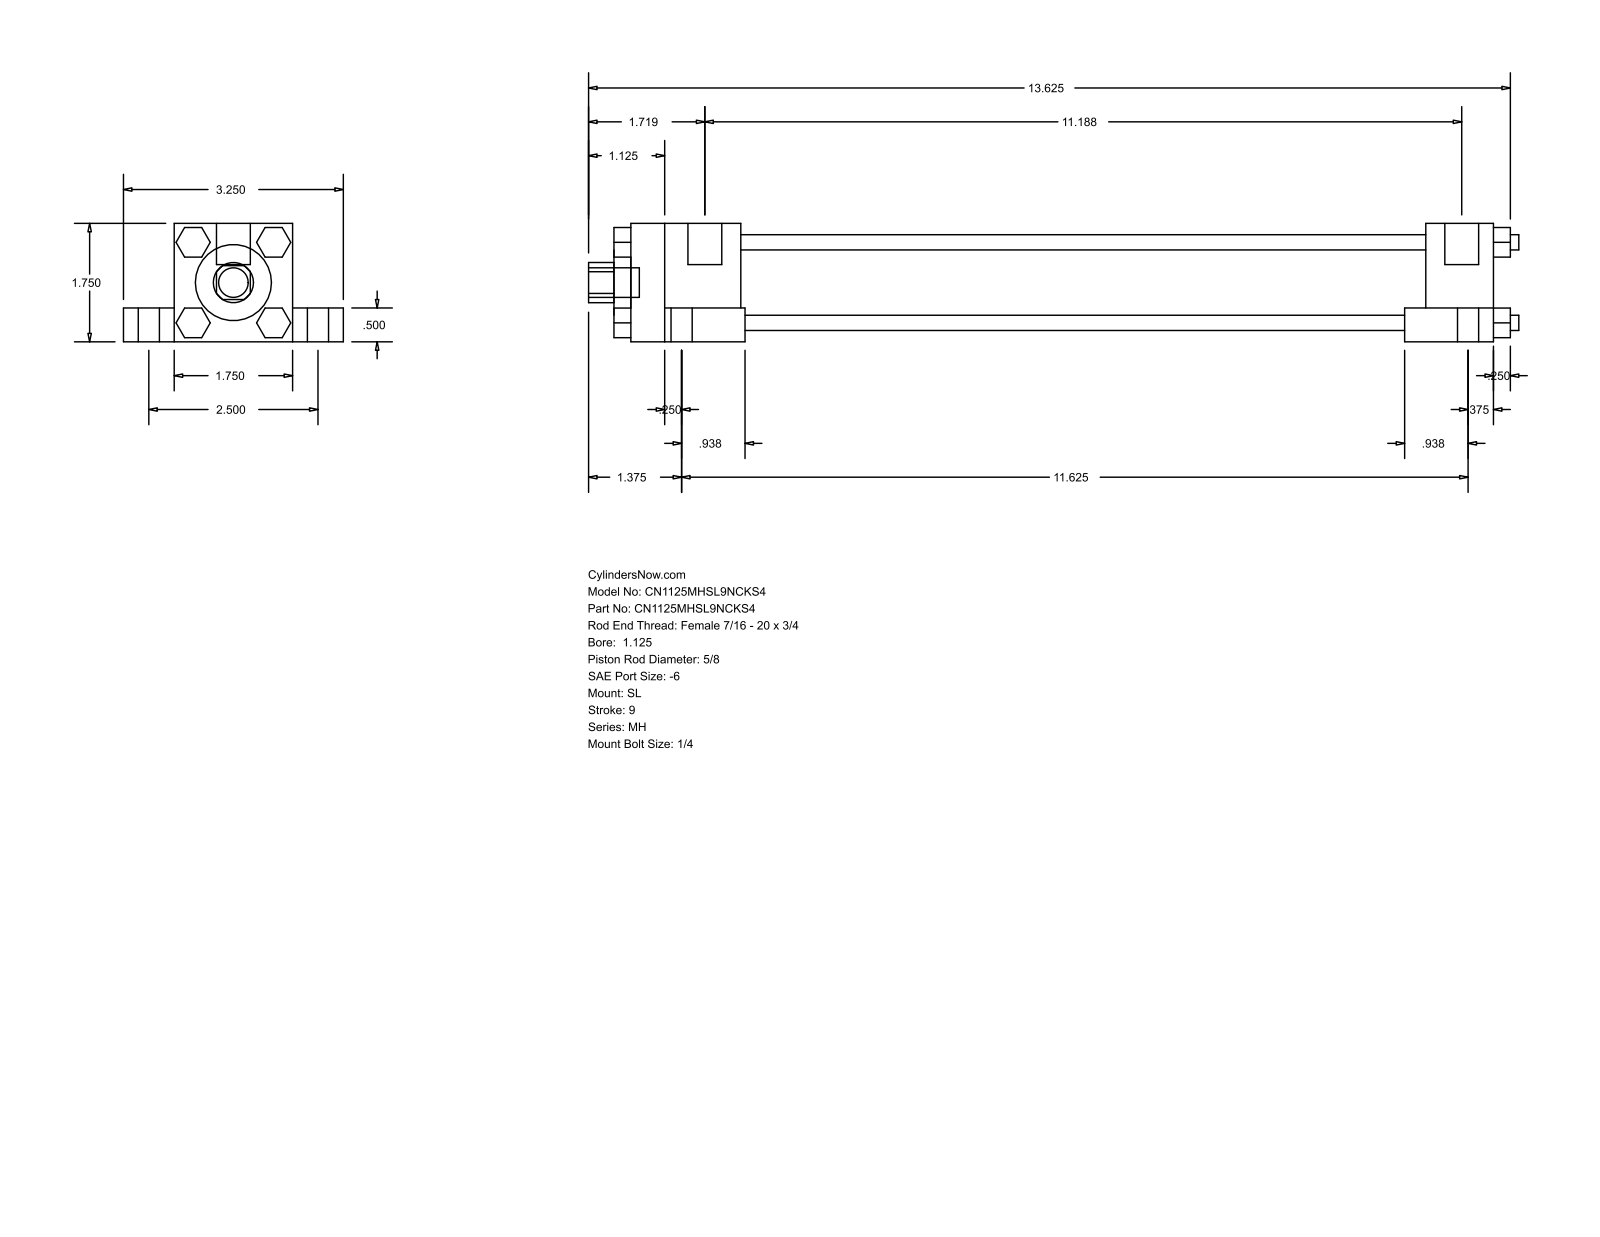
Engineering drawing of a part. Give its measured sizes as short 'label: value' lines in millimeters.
name: MH_SL__0112_0.625
written by: GSSL Pune (CONFIG_CONTROL_DESIGN)
unit: mm
bodies: 0 solids, 150 faces (114 planar, 36 cylindrical, 0 other)
size: 349.25 × 82.55 × 44.45
holes: 1× ⌀15.88, 1× ⌀28.57, 1× ⌀34.92
bosses: 4× ⌀14.29, 4× ⌀7.94, 4× ⌀5.71, 4× ⌀5.56, 2× ⌀12.7, 1× ⌀11.11
rounds: 1× R7.54
face distances: 44.46, 19.04, 12.7, 31.76, 63.5, 11.11, 33.34, 277.82, 257.17, 282.58
